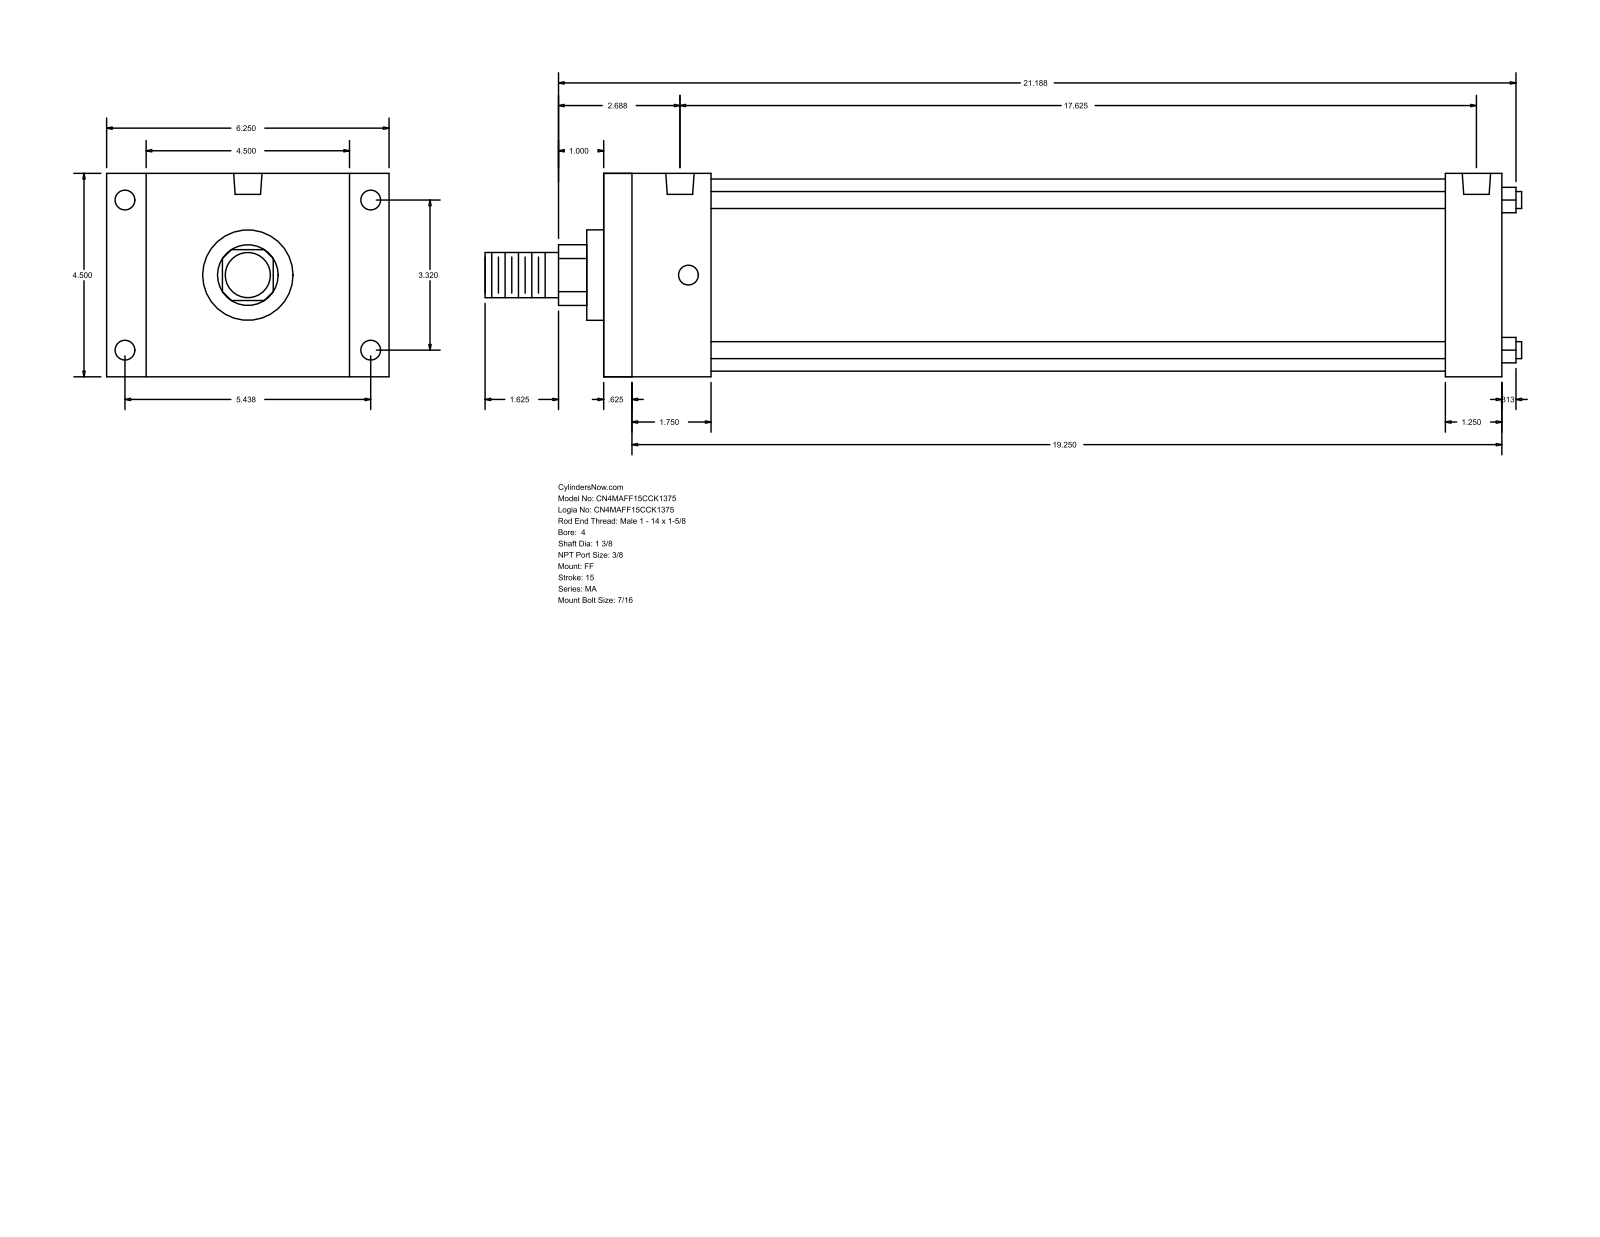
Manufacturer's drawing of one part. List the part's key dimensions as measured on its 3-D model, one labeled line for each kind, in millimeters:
Part name (STEP PRODUCT): MA_FF__0400_1.375
STEP written by: GSSL Pune (CONFIG_CONTROL_DESIGN)
Units: millimetres
Bodies: 0 solids, 92 faces (64 planar, 28 cylindrical, 0 other)
Overall size (bounding box): 582.61 × 158.75 × 114.3
Round holes (diameter × count): ⌀11.11 ×8, ⌀15.93 ×2
Round bosses / shafts (diameter × count): ⌀9.53 ×4, ⌀107.95 ×1, ⌀50.8 ×1, ⌀34.92 ×1, ⌀25.4 ×1
Partial cylindrical surfaces — rounded edges, fillets, slot ends (radius × count): R17.06 ×1
Main face-to-face distances: 114.3, 504.83, 15.87, 488.96, 22.23, 136.53, 473.08, 457.21, 31.75, 60.32
Hole centre spacings: 84.32, 138.12, 161.82, 438.15, 4.76, 4.77, 442.91, 442.92
